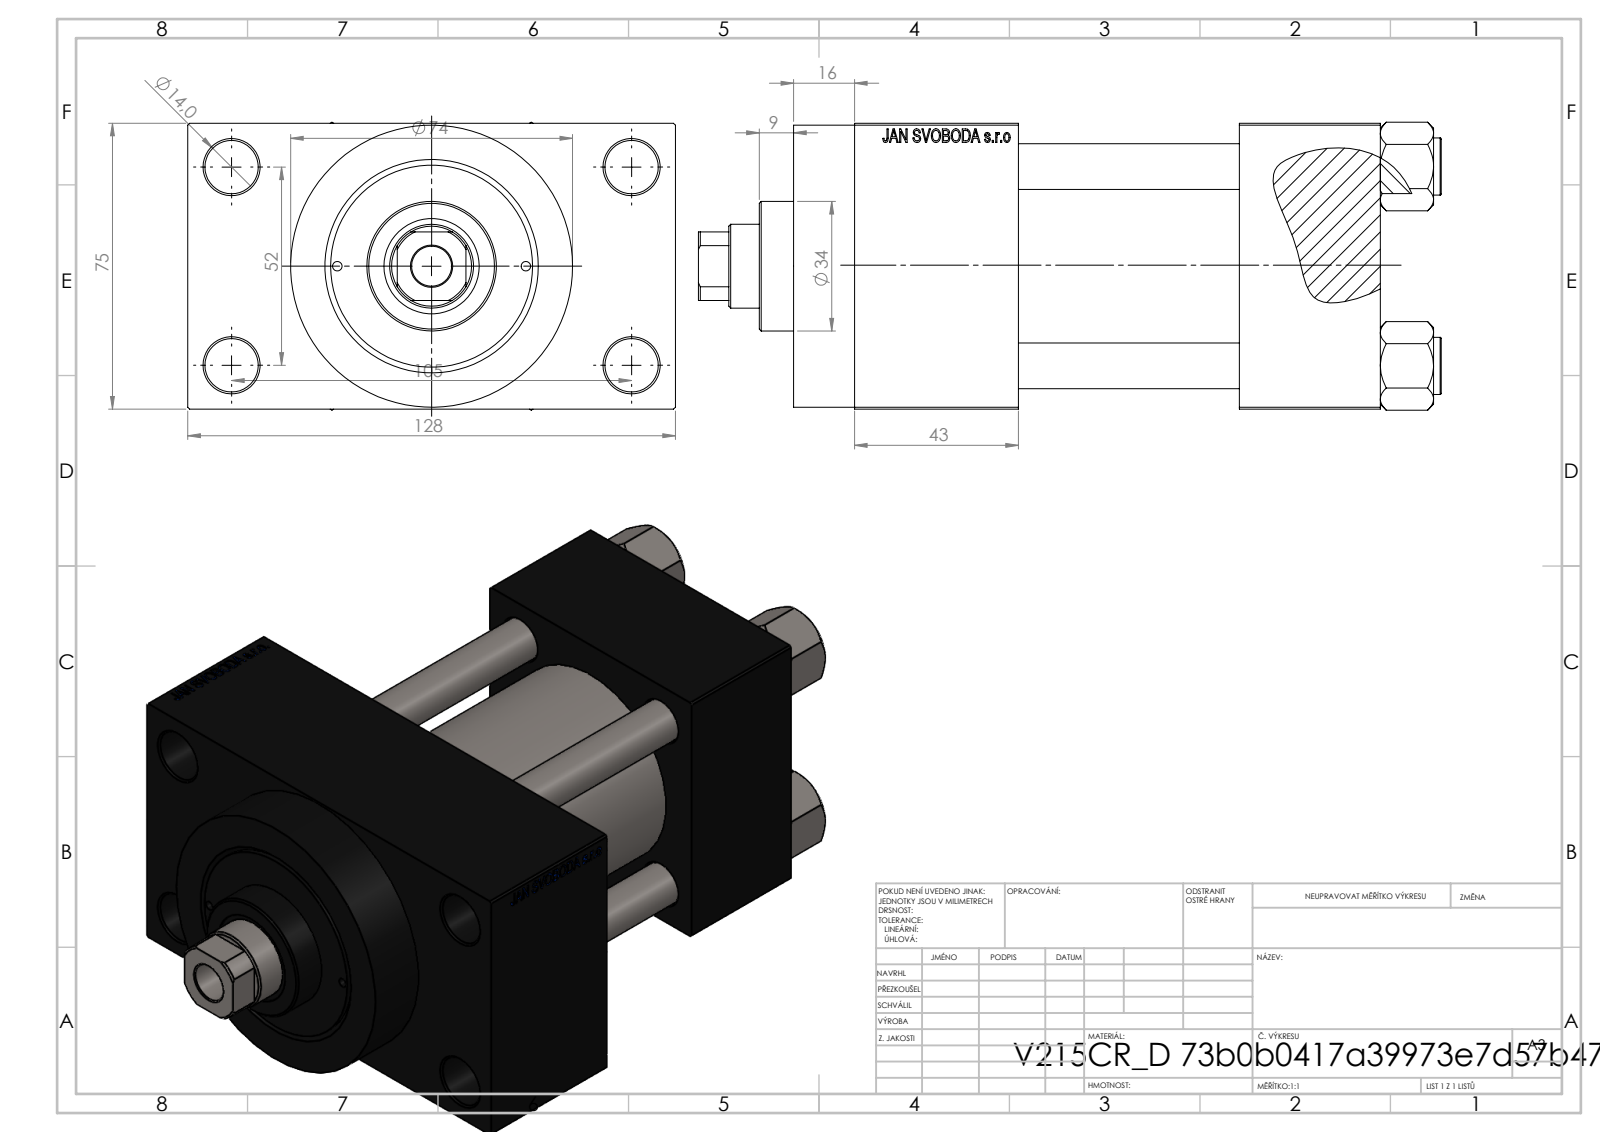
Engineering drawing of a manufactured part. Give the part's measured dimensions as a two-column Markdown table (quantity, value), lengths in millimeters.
| quantity | value |
| --- | --- |
| part name | V215_VC_A; NUT_M5_D; V215CR_D_Body; V215CR_D_TYCINKA (+1 more) |
| STEP written by | SolidWorks 2019 (CONFIG_CONTROL_DESIGN) |
| units | millimeters |
| bodies | 11 solids, 1111 faces (499 planar, 92 cylindrical, 520 other) |
| overall size | 195 × 128 × 75.54 |
| volume | 797 278 mm³ |
| surface area | 166 622 mm² |
| round holes (diameter × count) | 12 × 4, 14 × 4, 2.5 × 2, 7 × 2, 20.96 × 2, 30 × 2, 10.5 × 1, 22 × 1, 25 × 1, 41 × 1, 50 × 1, 53 × 1 |
| round bosses / shafts (diameter × count) | 15 × 4, 74 × 1, 56 × 1, 34 × 1 |
| partial cylindrical surfaces (radius × count) | 10.5 × 1 |
| main face-to-face distances | 75, 58, 37, 95, 26.5, 138, 101, 43, 101.5, 16 |
| hole center spacings | 26.19, 26.35, 36.98, 38.03, 52.3, 57.22, 58.43, 58.59 |
